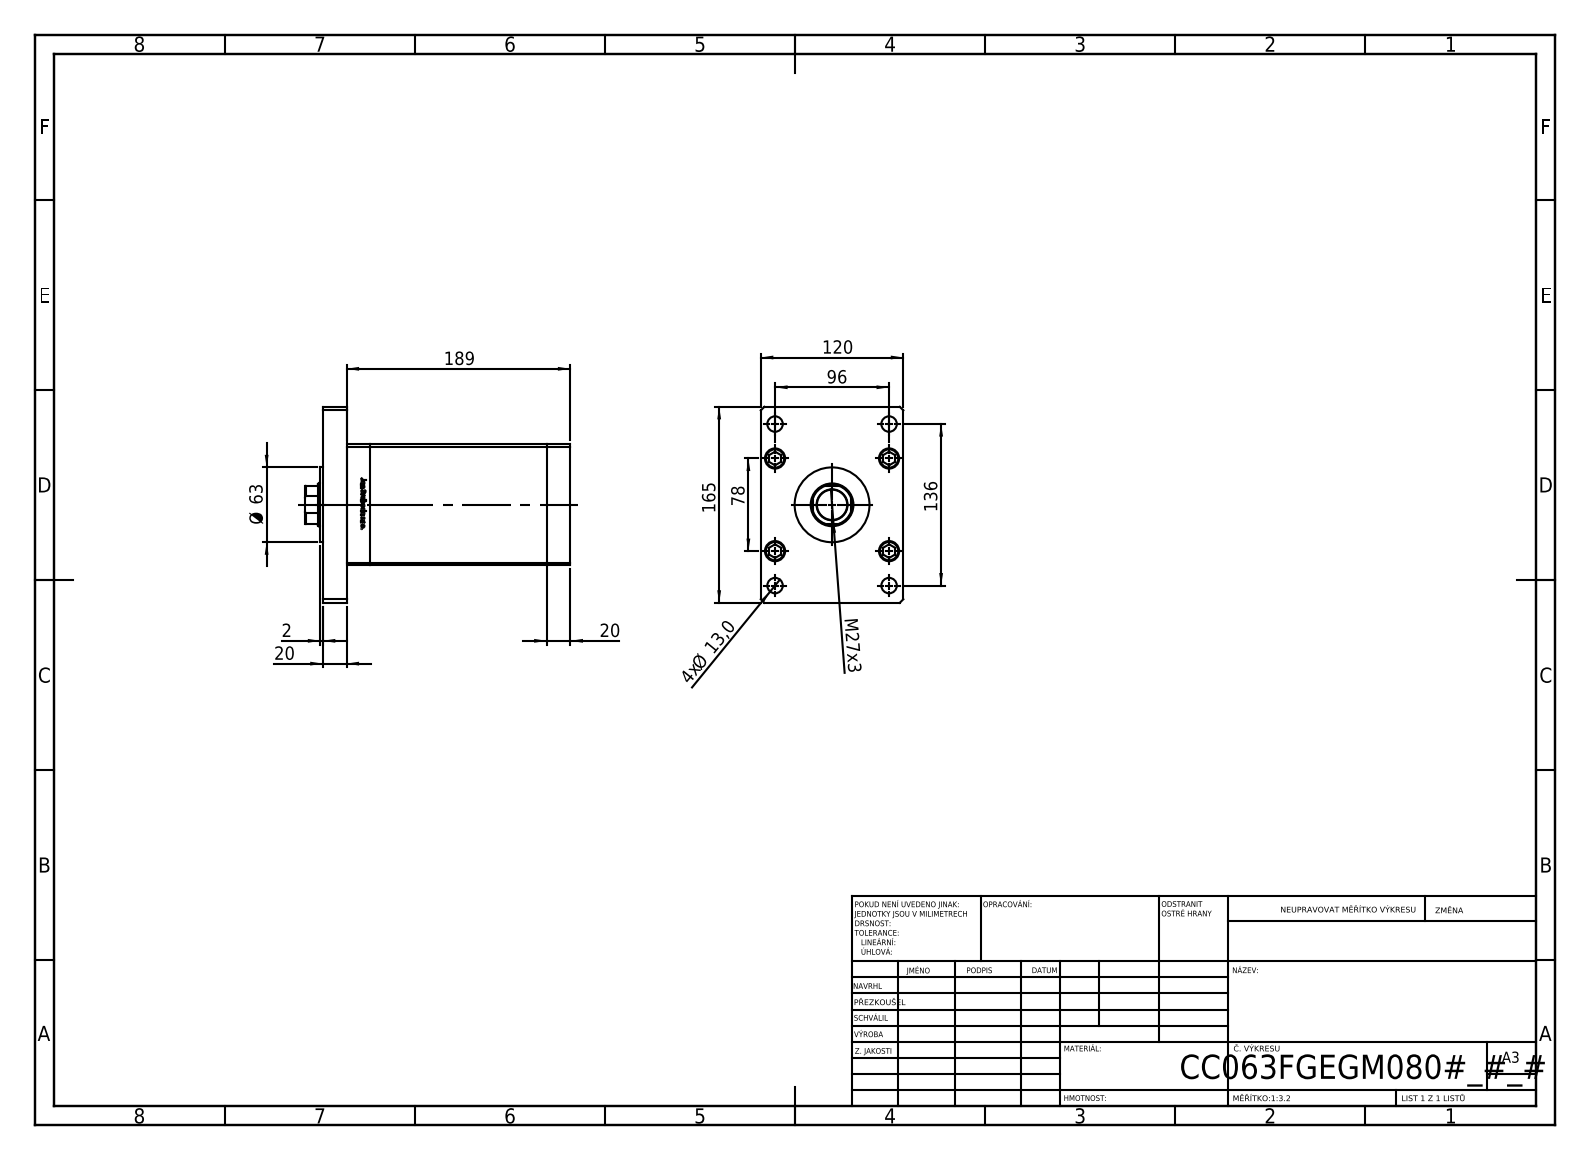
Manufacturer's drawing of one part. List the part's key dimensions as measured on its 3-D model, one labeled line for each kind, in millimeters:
Part name (STEP PRODUCT): V220C_F_MIDDLE; V220C_F; V220C_FRONT_F; V220C BACK_F (+2 more)
STEP written by: SolidWorks 2019 (CONFIG_CONTROL_DESIGN)
Units: millimetres
Bodies: 19 solids, 1311 faces (517 planar, 188 cylindrical, 606 other)
Overall size (bounding box): 223.5 × 165 × 120
Volume: 2 417 000 mm³ · Surface area: 321 367 mm²
Round holes (diameter × count): ⌀13.5 ×5, ⌀18 ×5, ⌀12 ×4, ⌀13 ×4, ⌀17 ×4, ⌀2 ×2, ⌀13.16 ×2, ⌀25.5 ×1, ⌀36 ×1, ⌀37.5 ×1
Round bosses / shafts (diameter × count): ⌀8 ×9, ⌀17 ×5, ⌀63 ×1
Partial cylindrical surfaces — rounded edges, fillets, slot ends (radius × count): R0.93 ×2, R17.5 ×1
Main face-to-face distances: 20, 168.5, 188.5, 120, 102, 148.5, 40, 208.5, 34.25, 22
Hole centre spacings: 41.5, 29, 61.85, 83.23, 96, 100.28, 107, 143.75
